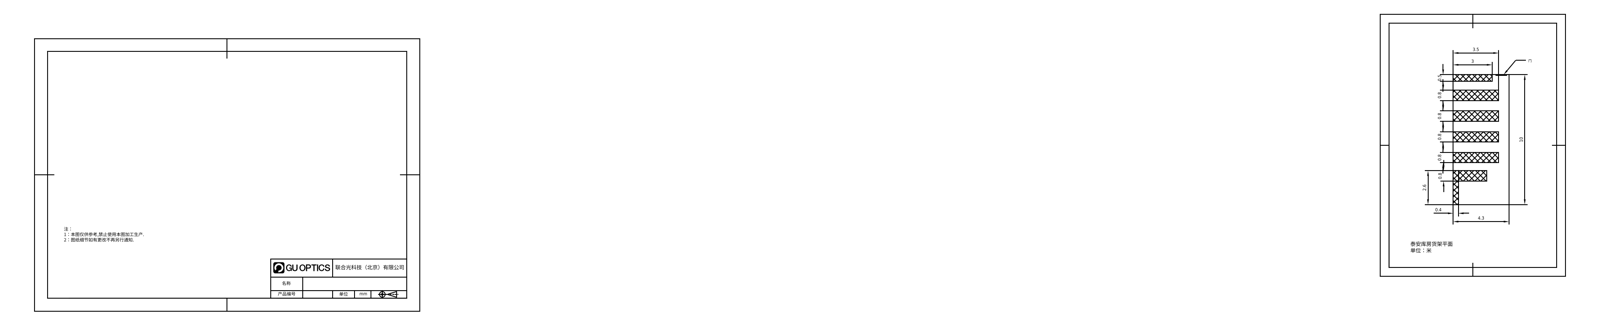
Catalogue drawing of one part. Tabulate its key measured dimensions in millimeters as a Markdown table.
| quantity | value |
| --- | --- |
| part name | 耐高温镜头 |
| STEP written by | SolidWorks 2020 (CONFIG_CONTROL_DESIGN) |
| units | millimeters |
| bodies | 28 solids, 190 faces (93 planar, 67 cylindrical, 30 other) |
| overall size | 254.19 × 20 × 20 |
| volume | 34 103 mm³ |
| surface area | 34 759 mm² |
| round holes (diameter × count) | 1.22 × 1, 3.6 × 1, 3.9 × 1, 4.5 × 1, 5.3 × 1, 5.8 × 1, 6.4 × 1, 6.7 × 1, 7.2 × 1, 7.4 × 1, 8 × 1, 8.5 × 1 |
| round bosses / shafts (diameter × count) | 20 × 1, 19.5 × 1, 17.5 × 1, 16.9 × 1, 16.7 × 1, 16.4 × 1, 14 × 1, 12 × 1 |
| main face-to-face distances | 2, 90.99, 91, 186.9, 188.9, 190.57, 188.57, 1.67, 97.9, 97.91 |
